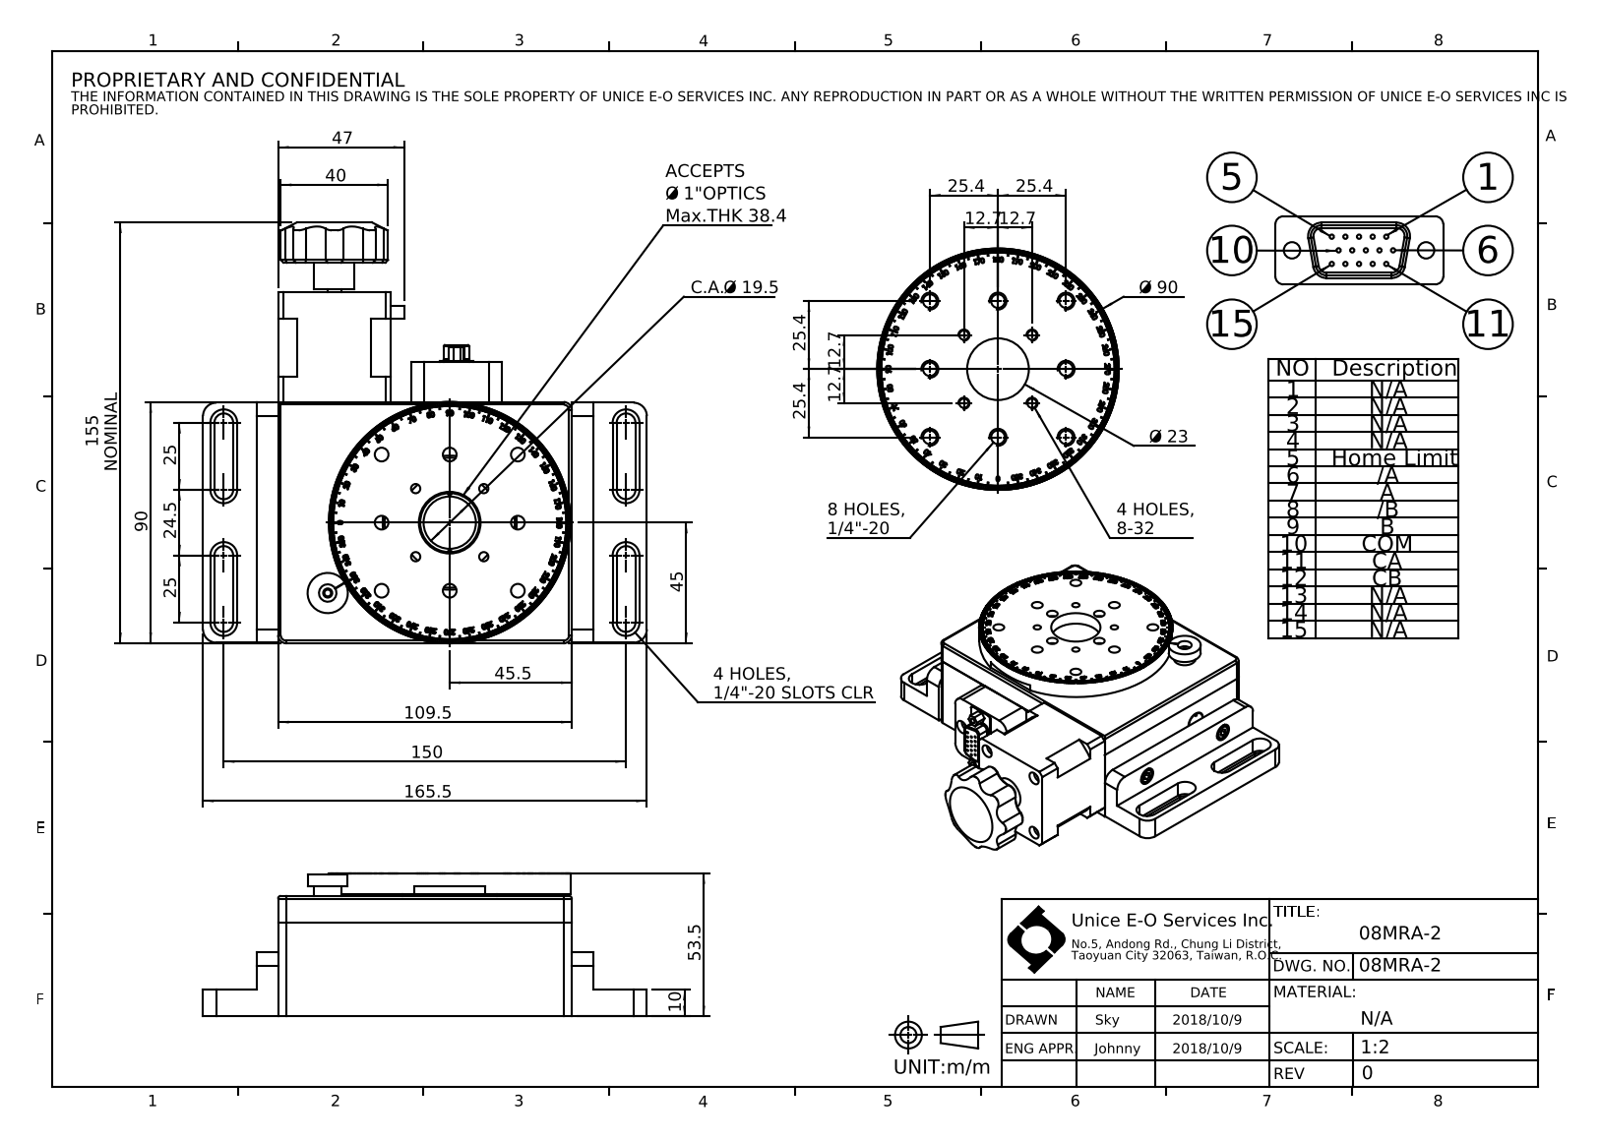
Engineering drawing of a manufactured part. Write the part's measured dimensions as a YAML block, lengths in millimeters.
part_name: "08MRA-2"
step_written_by: "SolidWorks 2016 (AUTOMOTIVE_DESIGN)"
units: millimeters
bodies: {solids: 0, faces: 1119, planar: 780, cylindrical: 248, other: 91}
overall_size: [165.5, 157, 53.5]
round_holes:
  - {diameter: 0.8, count: 15}
  - {diameter: 5.11, count: 8}
  - {diameter: 6.5, count: 7}
  - {diameter: 3.4, count: 5}
  - {diameter: 2.9, count: 4}
  - {diameter: 3.45, count: 4}
  - {diameter: 5, count: 4}
  - {diameter: 5.5, count: 4}
  - {diameter: 6.1, count: 4}
  - {diameter: 1.5, count: 2}
  - {diameter: 2.5, count: 2}
  - {diameter: 3.3, count: 2}
round_bosses_or_shafts:
  - {diameter: 15, count: 2}
  - {diameter: 7, count: 2}
  - {diameter: 90, count: 1}
  - {diameter: 49, count: 1}
  - {diameter: 10, count: 1}
partial_cylinders:
  - {radius: 5, count: 18}
  - {radius: 0.5, count: 8}
  - {radius: 3.5, count: 8}
  - {radius: 4, count: 8}
  - {radius: 7.41, count: 8}
  - {radius: 1, count: 4}
  - {radius: 1.5, count: 4}
  - {radius: 2, count: 4}
face_to_face_distances: [45, 8, 0.5, 8.5, 109.5, 10, 53.5, 45.5, 35, 90]
hole_center_spacings: [2.84, 17.96, 25.4, 40.16, 4.58, 5.08, 2.54, 6.84]
